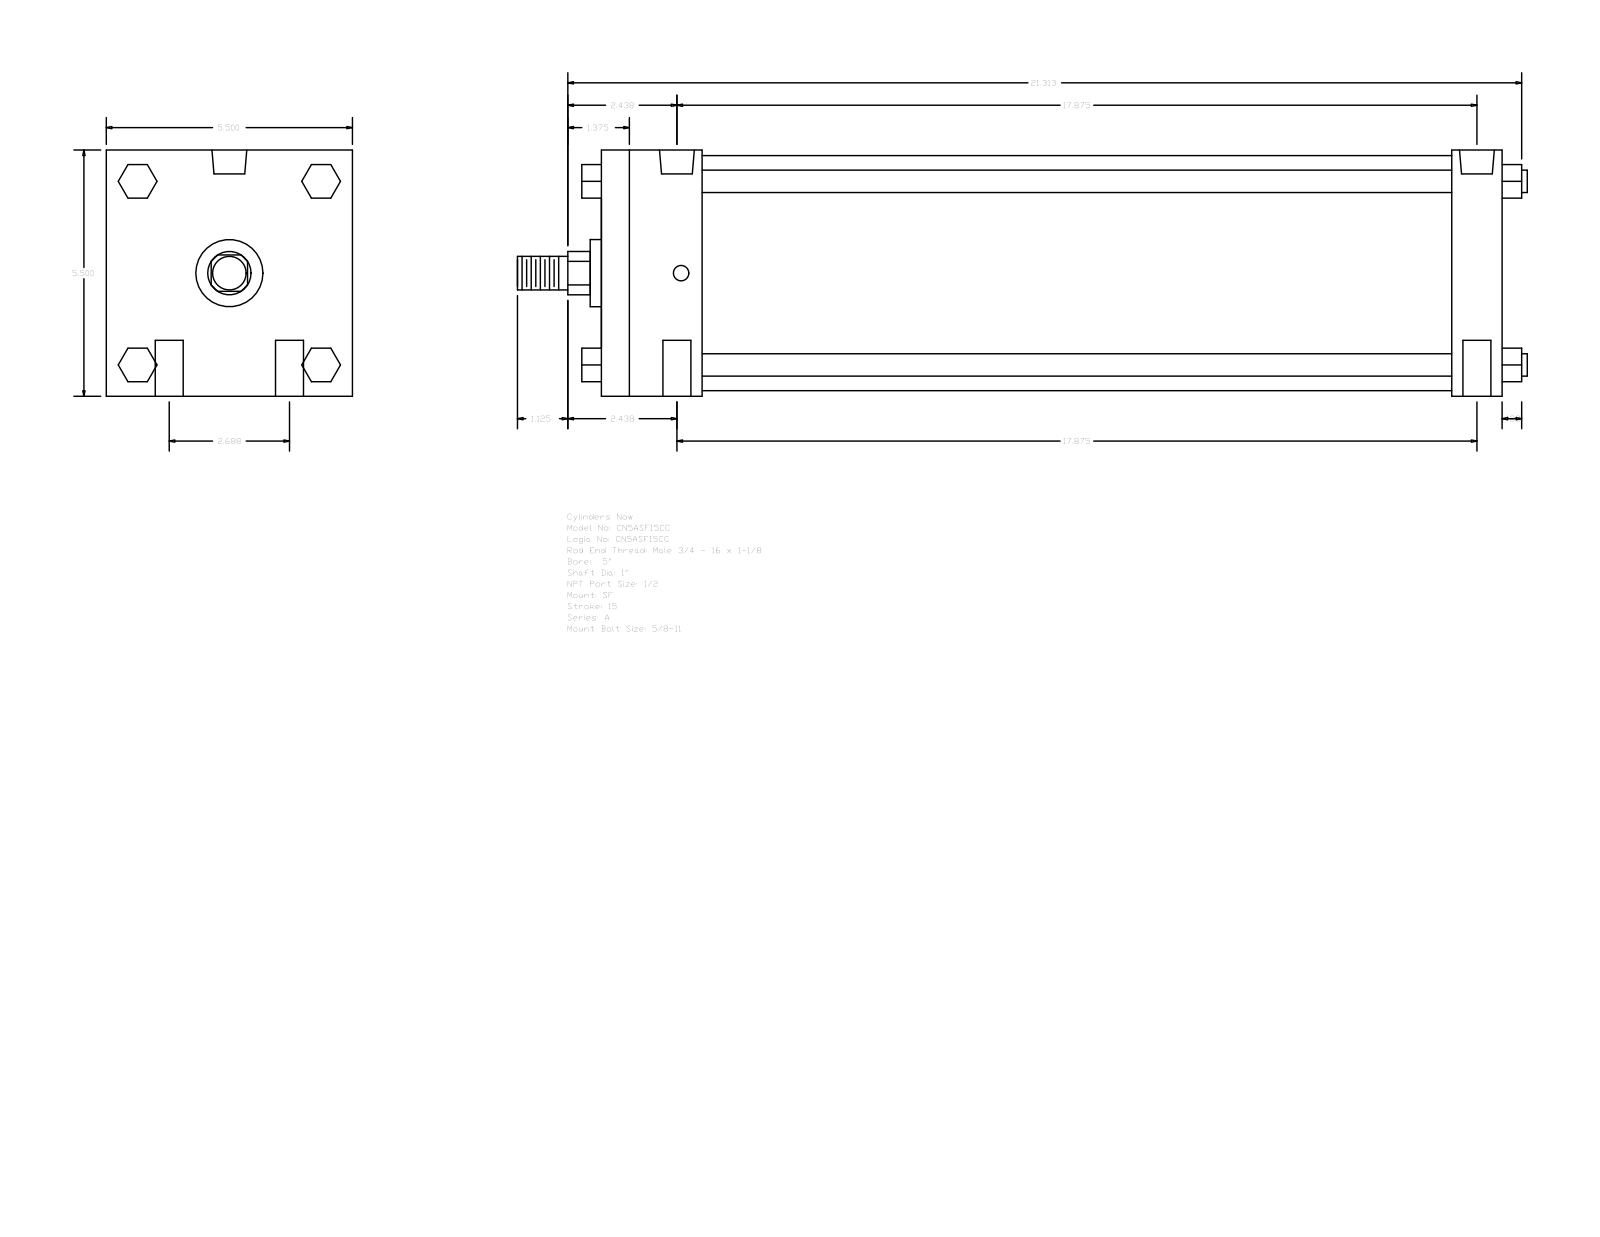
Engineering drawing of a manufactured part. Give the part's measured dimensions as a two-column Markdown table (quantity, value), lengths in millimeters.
| quantity | value |
| --- | --- |
| part name | A_SF__0500_1 |
| STEP written by | GSSL Pune (CONFIG_CONTROL_DESIGN) |
| units | millimeters |
| bodies | 0 solids, 124 faces (94 planar, 30 cylindrical, 0 other) |
| overall size | 573.09 × 139.7 × 139.7 |
| round holes (diameter × count) | 15.88 × 4, 8.73 × 2, 19.77 × 2 |
| round bosses / shafts (diameter × count) | 12.7 × 4, 133.35 × 1, 38.1 × 1, 25.4 × 1, 19.05 × 1 |
| partial cylindrical surfaces (radius × count) | 12.29 × 1 |
| main face-to-face distances | 139.7, 511.18, 57.15, 482.6, 425.45, 454.03, 28.58, 19.05, 52.07, 90.18 |
| hole center spacings | 34.13, 455.31, 454.03, 68.26, 459.13, 449.25 |
